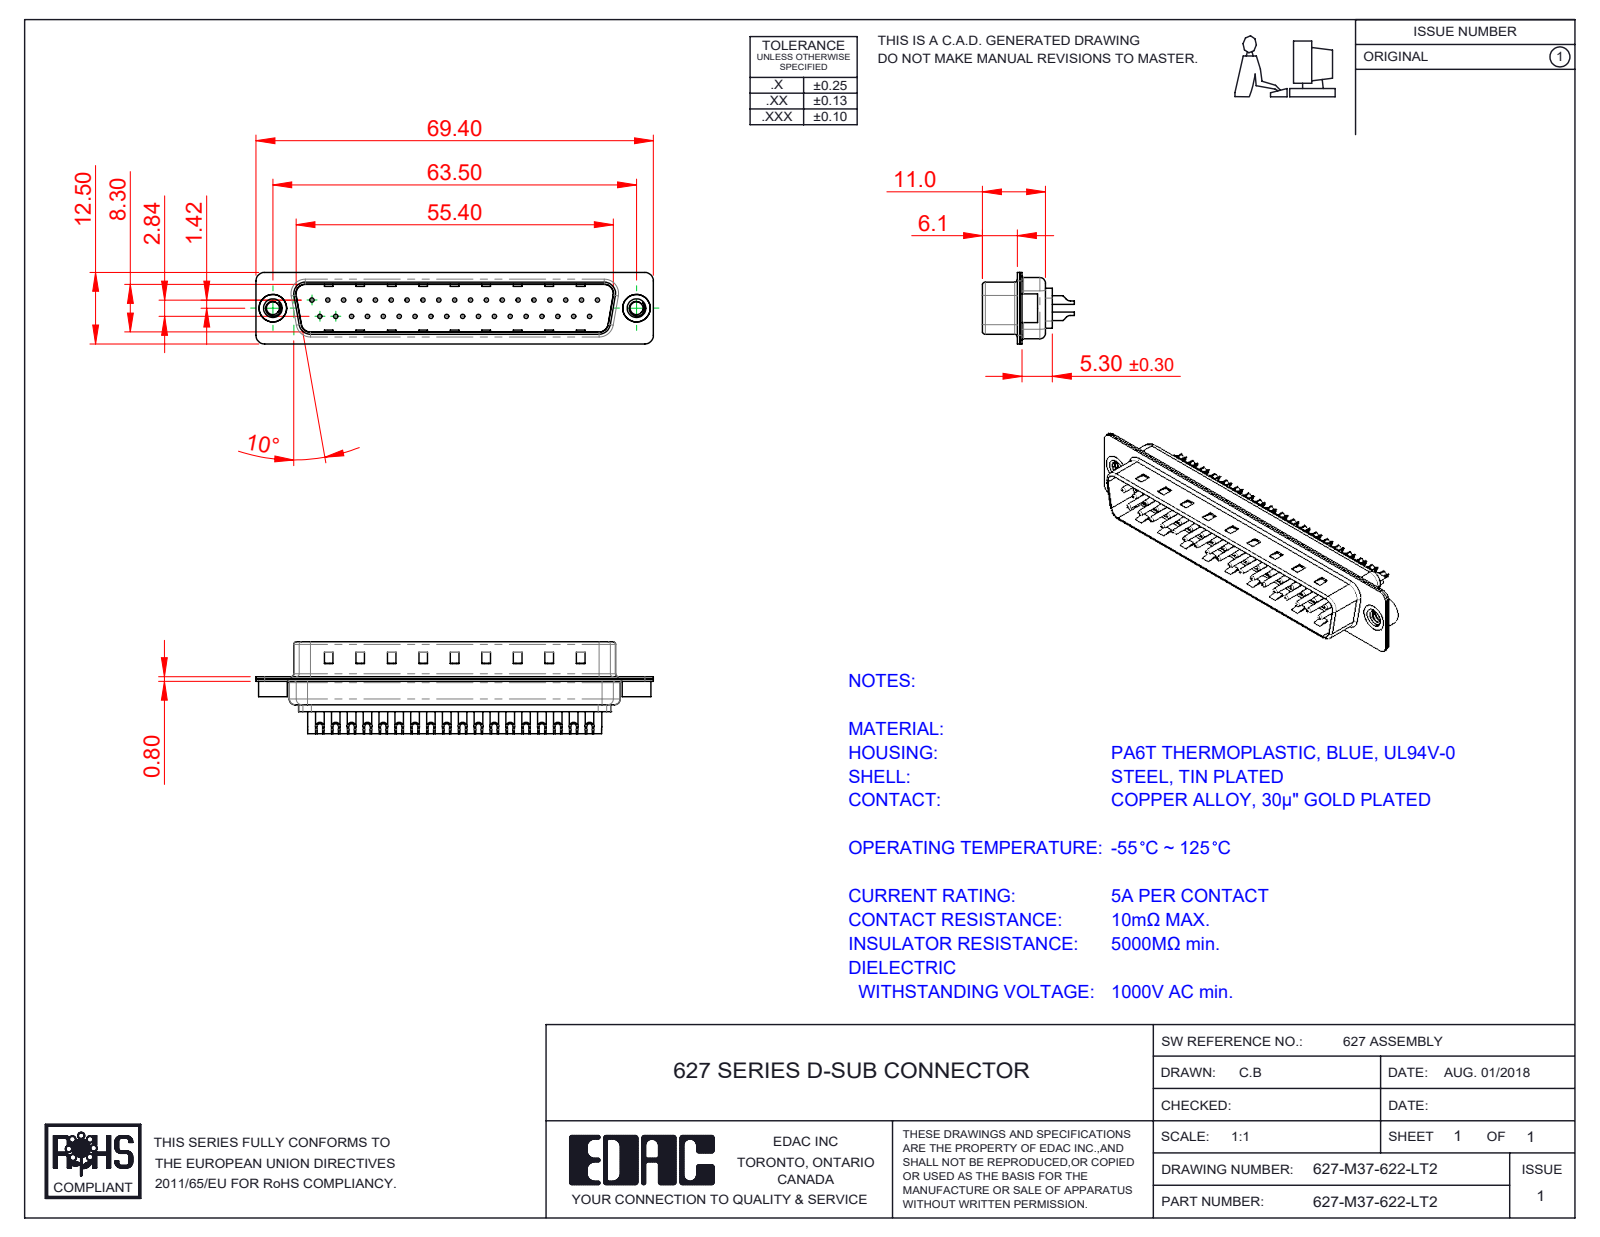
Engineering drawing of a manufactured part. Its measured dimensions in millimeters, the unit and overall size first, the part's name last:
Units: millimetres
Overall size (bounding box): 69.4 × 16.05 × 12.5
Round holes (diameter × count): ⌀0.75 ×37, ⌀1 ×37, ⌀1.6 ×37, ⌀2 ×37, ⌀2.26 ×2, ⌀4 ×2, ⌀4.8 ×2
Round bosses / shafts (diameter × count): ⌀1.5 ×37, ⌀5 ×2, ⌀4.9 ×2
Partial cylindrical surfaces — rounded edges, fillets, slot ends (radius × count): R1.5 ×16, R2 ×12, R0.5 ×8, R1.6 ×8, R1 ×6, R0.25 ×4, R0.6 ×4, R0.65 ×4
Main face-to-face distances: 0.4, 0.8, 9.5, 9.1, 8.7, 9.9, 1.2, 0.75, 0.35, 5.7
Hole centre spacings: 2.77, 5.54, 3.16, 8.31, 11.08, 13.85, 16.62, 19.39
Volume: 3 853 mm³ · Surface area: 9 616 mm²
Bodies: 42 solids, 1781 faces (536 planar, 733 cylindrical, 512 other)
Part name (STEP PRODUCT): 627M Shell Rear_37 Contacts; 627M 4-40 Threaded Rivet; 627M Housing_37 Contacts; 627M Contact Row 2_22 (+3 more)
STEP written by: SolidWorks 2020 (CONFIG_CONTROL_DESIGN)
